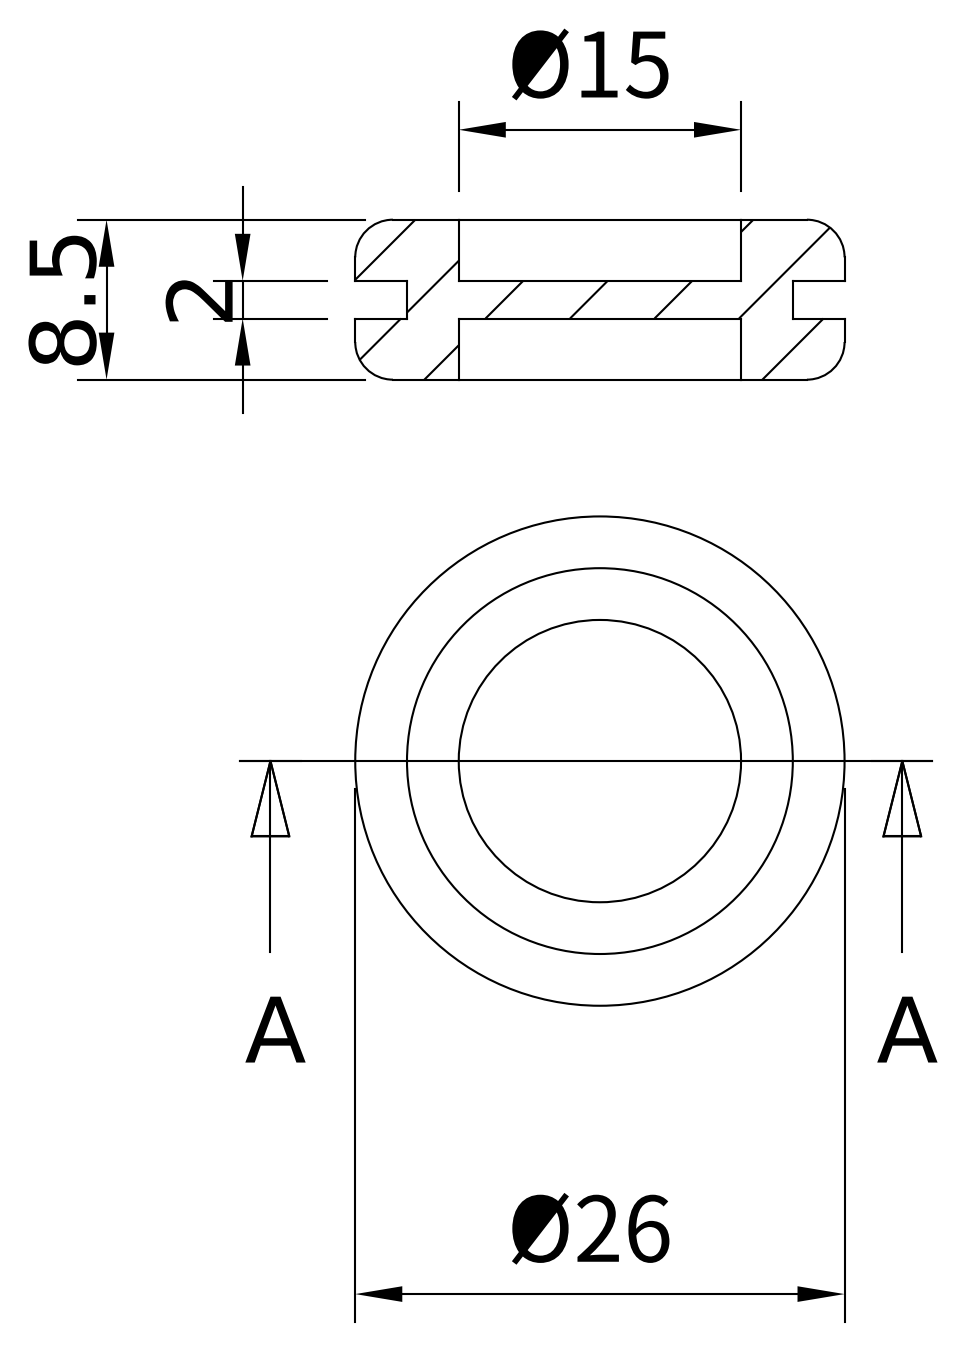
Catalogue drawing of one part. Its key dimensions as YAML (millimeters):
part_name: "CMEGC0000017"
step_written_by: "Autodesk Inventor 2019 (AUTOMOTIVE_DESIGN)"
units: millimeters
bodies: {solids: 1, faces: 13, planar: 6, cylindrical: 5, other: 2}
overall_size: [26, 26, 8.5]
volume: 2827
surface_area: 2286
round_holes:
  - {diameter: 15, count: 1}
round_bosses_or_shafts:
  - {diameter: 26, count: 1}
  - {diameter: 20.5, count: 1}
face_to_face_distances: [3.25, 5.25, 2, 8.5]
